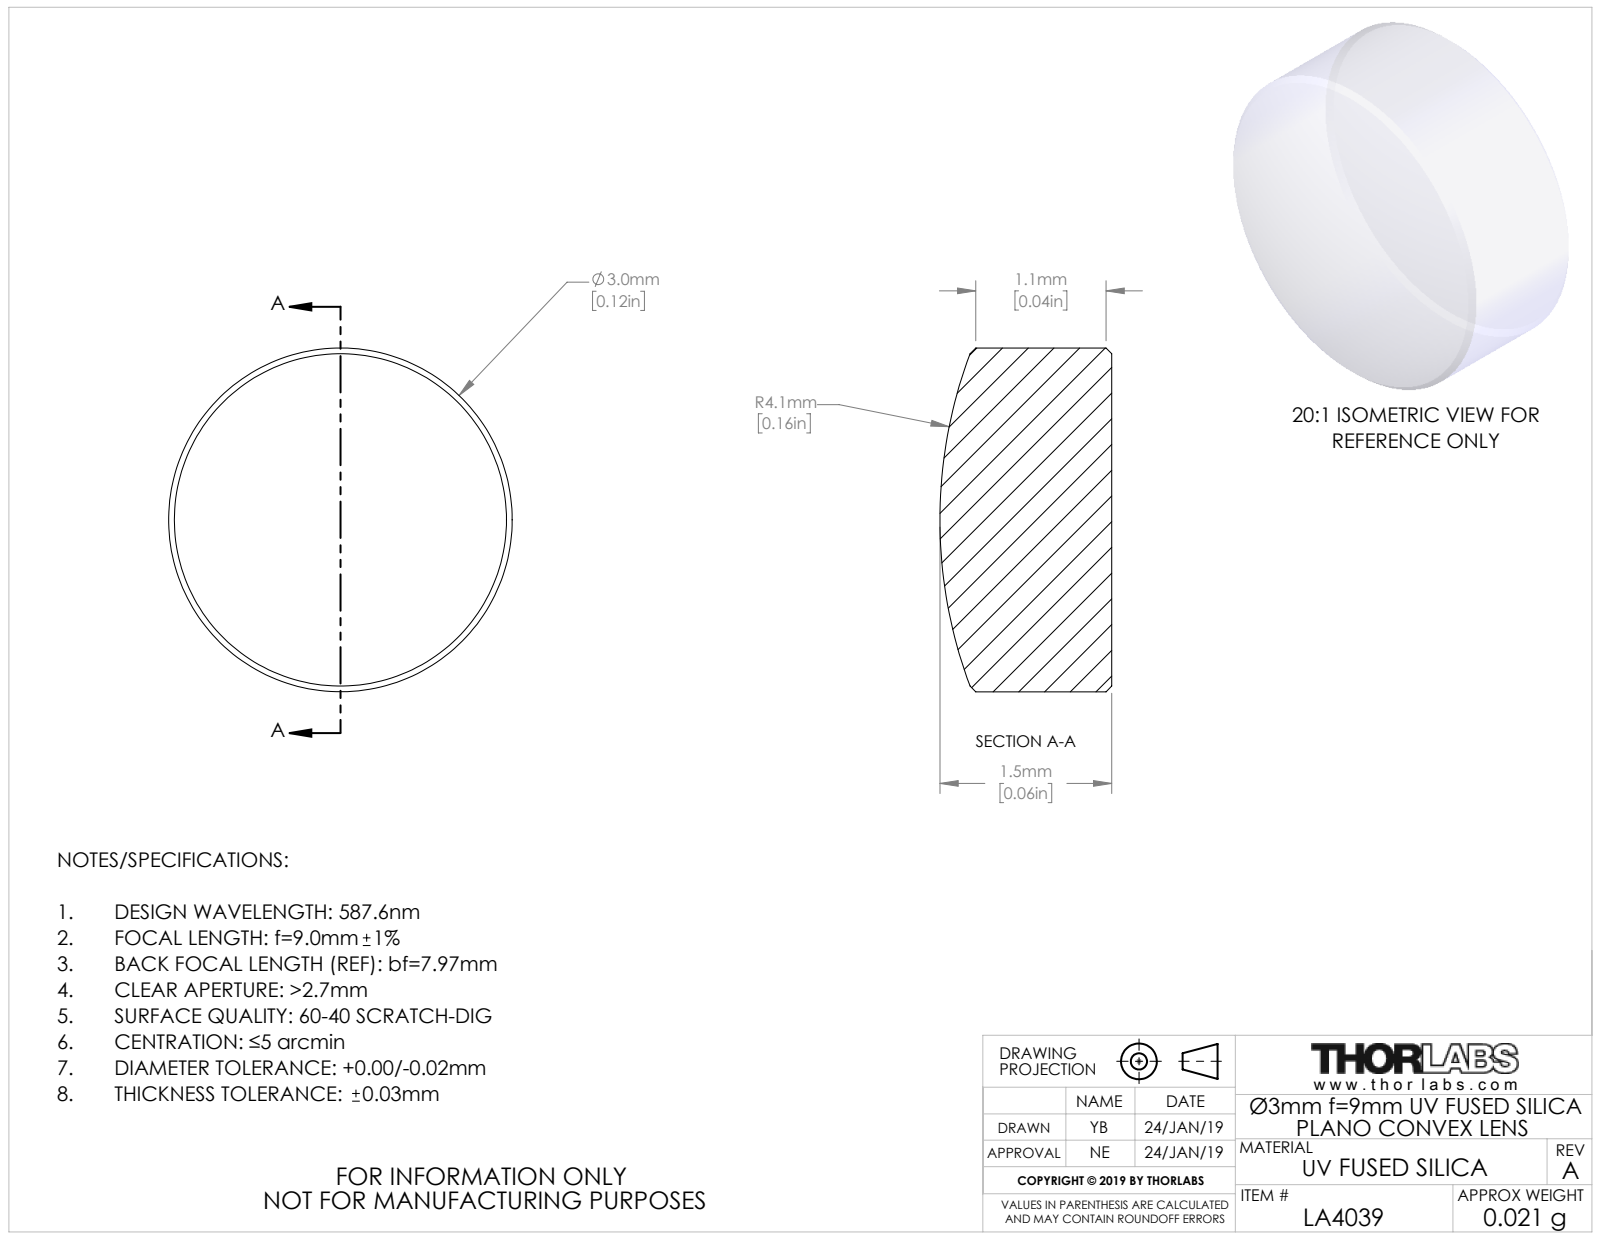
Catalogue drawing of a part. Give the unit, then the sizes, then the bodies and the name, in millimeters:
Units: millimetres
Overall size (bounding box): 3 × 3 × 1.5
Round bosses / shafts (diameter × count): ⌀3 ×1
Volume: 10 mm³ · Surface area: 25 mm²
Bodies: 1 solid, 9 faces (1 planar, 2 cylindrical, 6 other)
Part name (STEP PRODUCT): TTN162797-E0W
STEP written by: SolidWorks 2018 (CONFIG_CONTROL_DESIGN)
